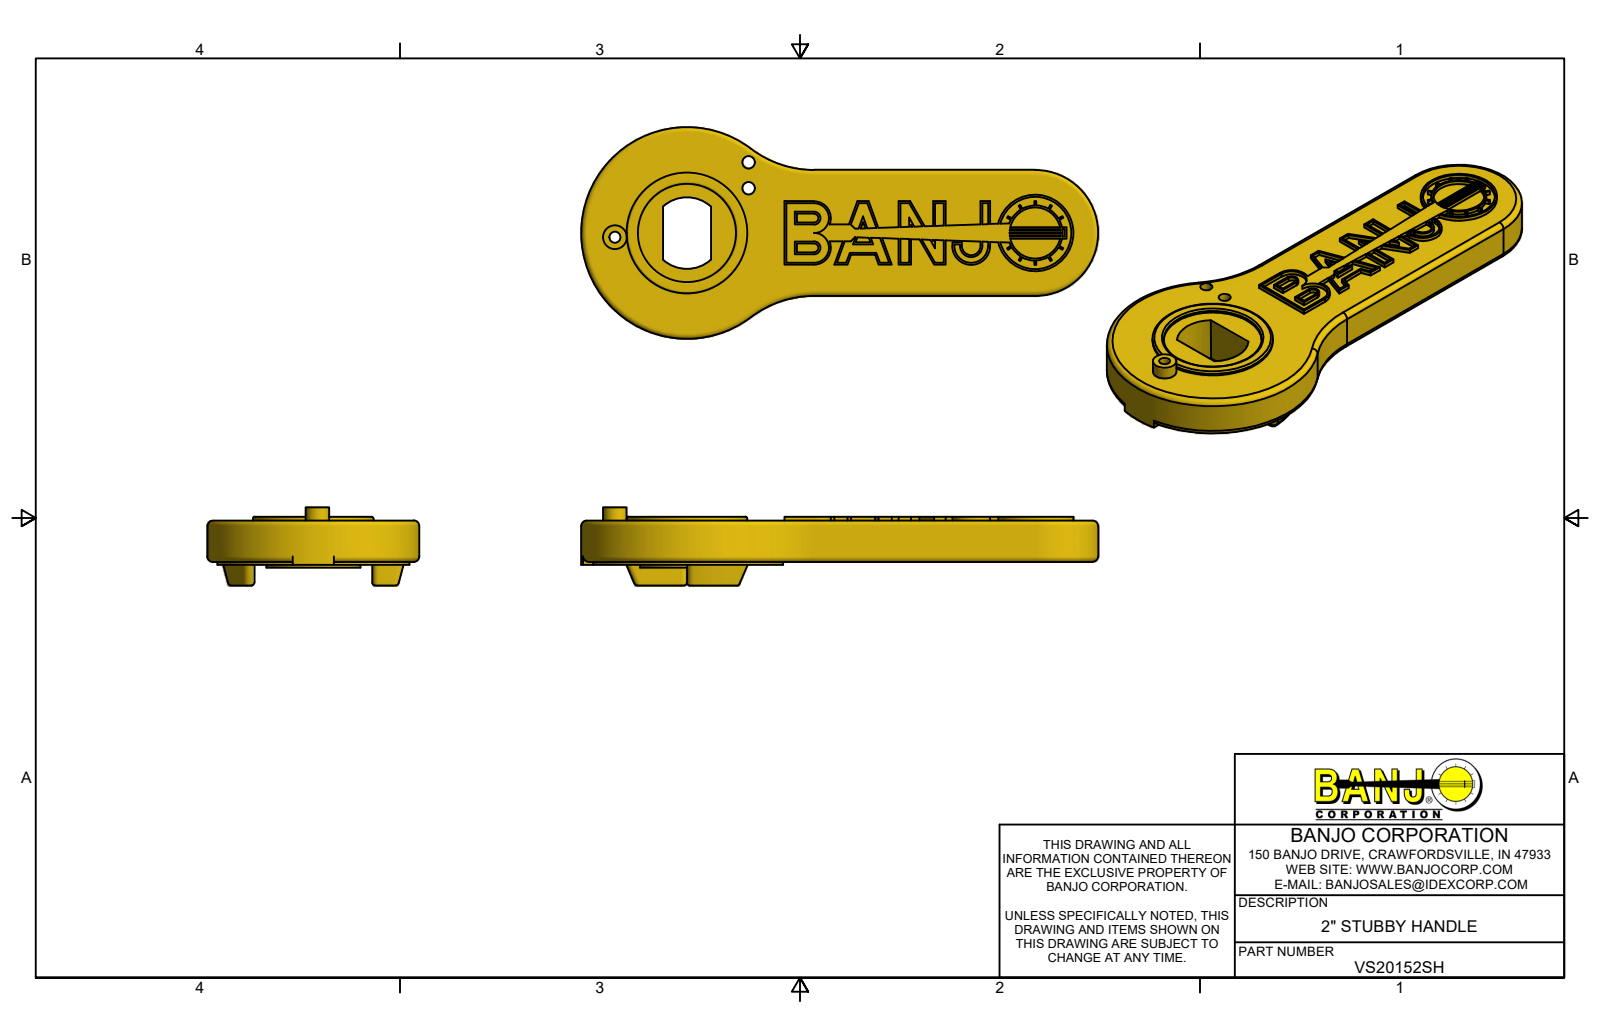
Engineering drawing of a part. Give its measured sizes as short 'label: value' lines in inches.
name: VS20152SH
written by: Autodesk Inventor 2013 (AUTOMOTIVE_DESIGN)
unit: in
bodies: 1 solid, 872 faces (591 planar, 66 cylindrical, 215 other)
size: 5.495 × 2.25 × 0.83
volume: 3.143 in³; area: 26.99 in²
holes: 2× ⌀0.13, 1× ⌀0.118, 1× ⌀0.544, 1× ⌀0.77, 1× ⌀1.04
bosses: 1× ⌀2.06, 1× ⌀1.28, 1× ⌀1, 1× ⌀0.81, 1× ⌀0.25
rounds: 8× R0.06, 6× R0.03, 2× R0.047, 2× R0.068, 2× R0.125, 2× R0.159, 2× R0.179, 2× R1
face distances: 0.27, 0.2, 0.47, 0.03, 0.17, 0.51, 0.31, 0.04, 1.34, 0.44
hole spacings: 0.276, 0.767, 0.809, 0.996, 1.513, 1.628, 3.081, 3.136
